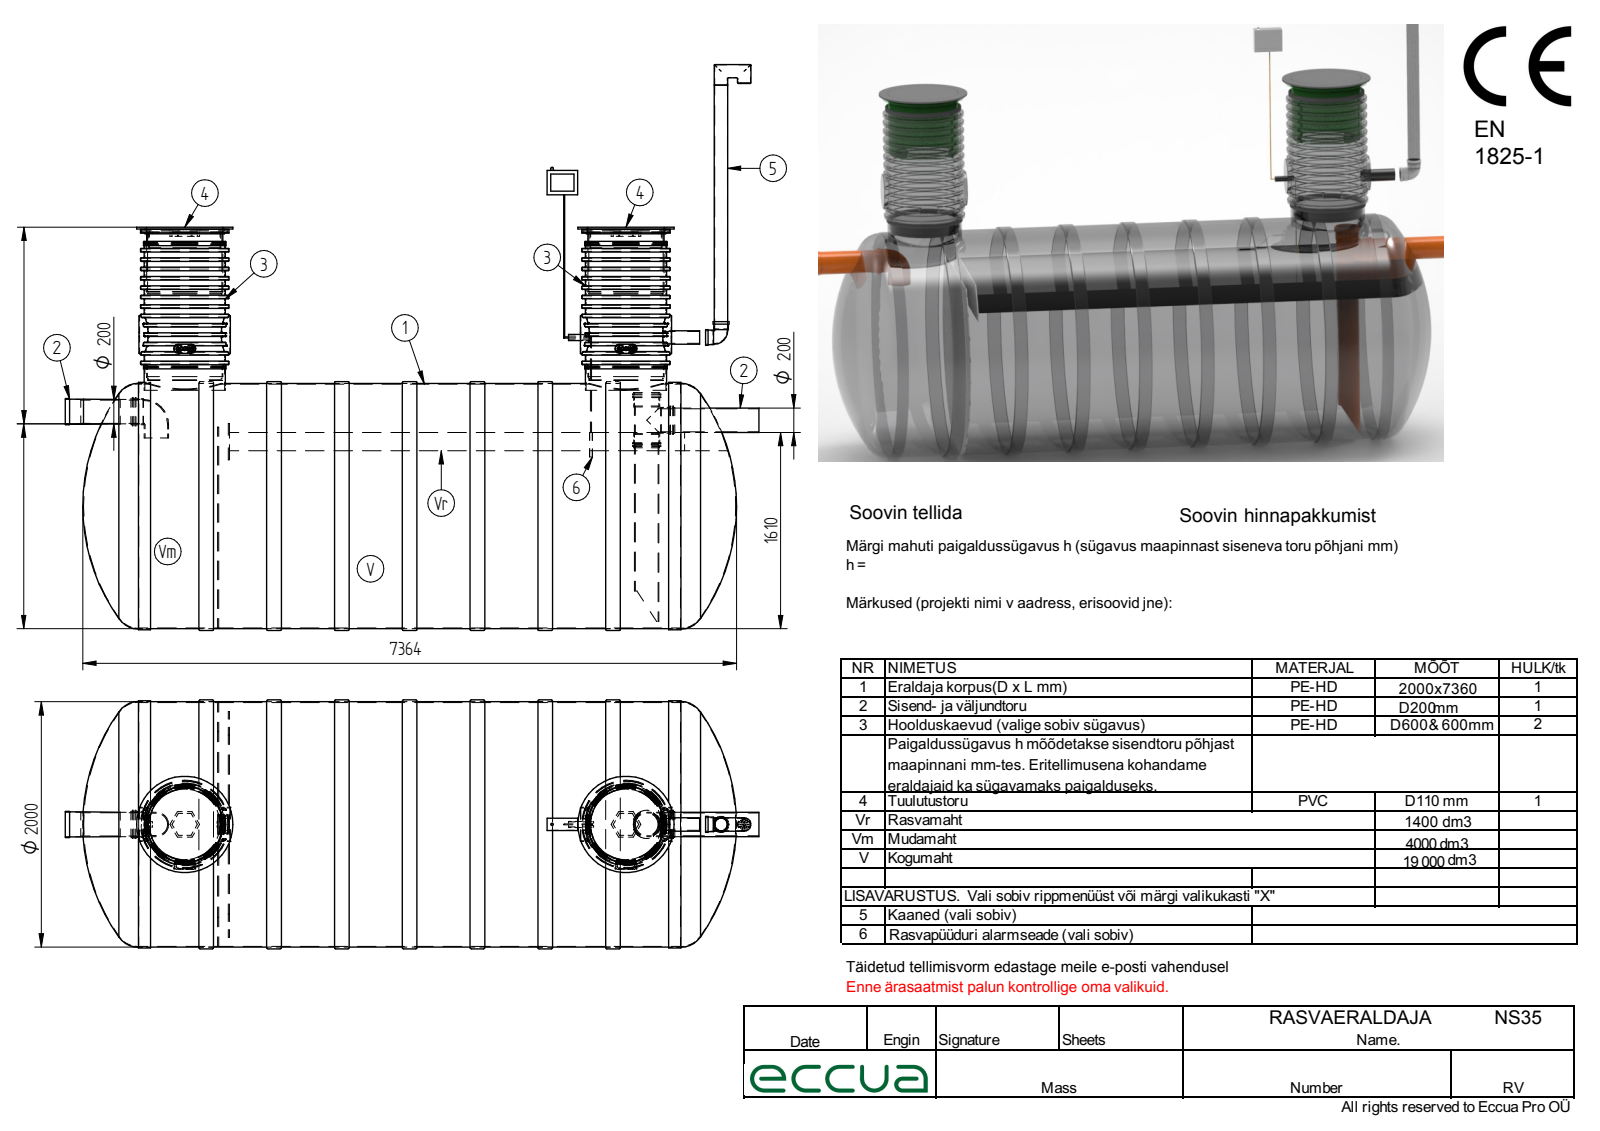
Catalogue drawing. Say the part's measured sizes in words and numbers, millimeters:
The part is named "Rasvaeraldaja NS35; 2381.003; rasvaeraldaja NS35_silinder; 2000 Ribi (+8 more)". Its 3-D file was written by "Solid Edge (AUTOMOTIVE_DESIGN)". It is 52 solids with 1262 faces: 489 planar, 392 cylindrical and 381 other. Overall it measures 7759 by 4132.62 by 2618.53 millimeters. Its volume is 3 897 000 000 cubic millimeters and its surface area 264 900 000 square millimeters. Round holes: 31 of diameter 10, 3 of diameter 103.2, 3 of diameter 200, 2 of diameter 6, 2 of diameter 100, 2 of diameter 188, 2 of diameter 220, 2 of diameter 595, 2 of diameter 600, 2 of diameter 609, 2 of diameter 615, 2 of diameter 630. Round bosses or shafts: 4 of diameter 110, 3 of diameter 212, 3 of diameter 8.5, 2 of diameter 790, 2 of diameter 725, 2 of diameter 678.5, 2 of diameter 665, 2 of diameter 650. Partial cylindrical surfaces (rounded edges, fillets, slot ends): 8 of radius 5, 8 of radius 30, 8 of radius 35, 6 of radius 3, 2 of radius 135, 2 of radius 140, 2 of radius 289.9, 1 of radius 130. The main face-to-face distances are 150, 8, 195, 45, 5, 88, 1126, 1874, 1724, 1679. The hole center spacings are 40, 72.08, 49.88, 62.55, 34.71, 17.8, 26.75, 77.99.
